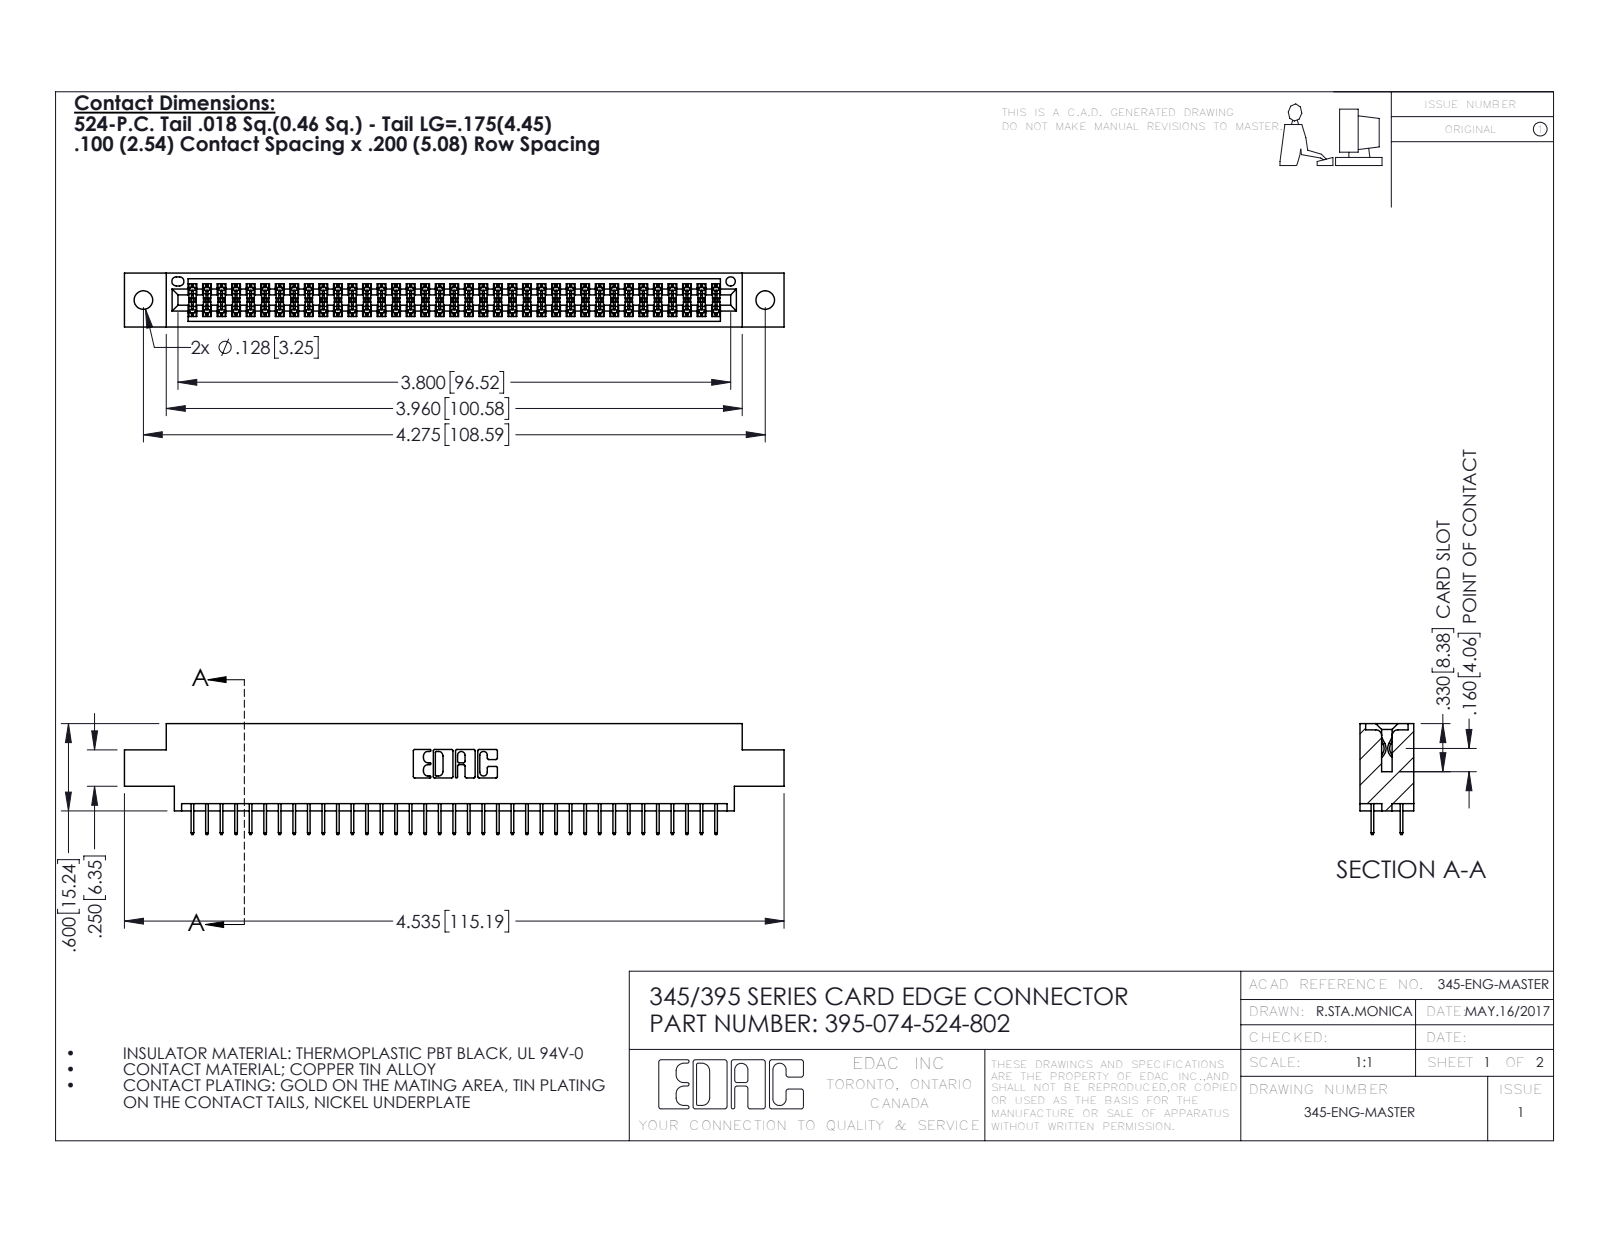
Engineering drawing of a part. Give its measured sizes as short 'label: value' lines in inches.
name: 395-074-524-802; 345 Part_0.170 Offset - 0.128 Dia; 345-292-001_345-293-124
written by: SolidWorks 2016 (CONFIG_CONTROL_DESIGN)
unit: in
bodies: 75 solids, 4126 faces (2970 planar, 1156 cylindrical, 0 other)
size: 4.535 × 0.762 × 0.37
volume: 0.664 in³; area: 24.12 in²
holes: 2× ⌀0.128, 1× ⌀0.064
rounds: 111× R0.006, 22× R0.01, 6× R0.007, 6× R0.031, 3× R0.026, 2× R0.014, 2× R0.019, 2× R0.022
face distances: 0.072, 0.298, 0.37, 0.2, 0.098, 0.272, 0.025, 0.225, 0.175, 0.072
hole spacings: 0.27, 4.039, 4.275
